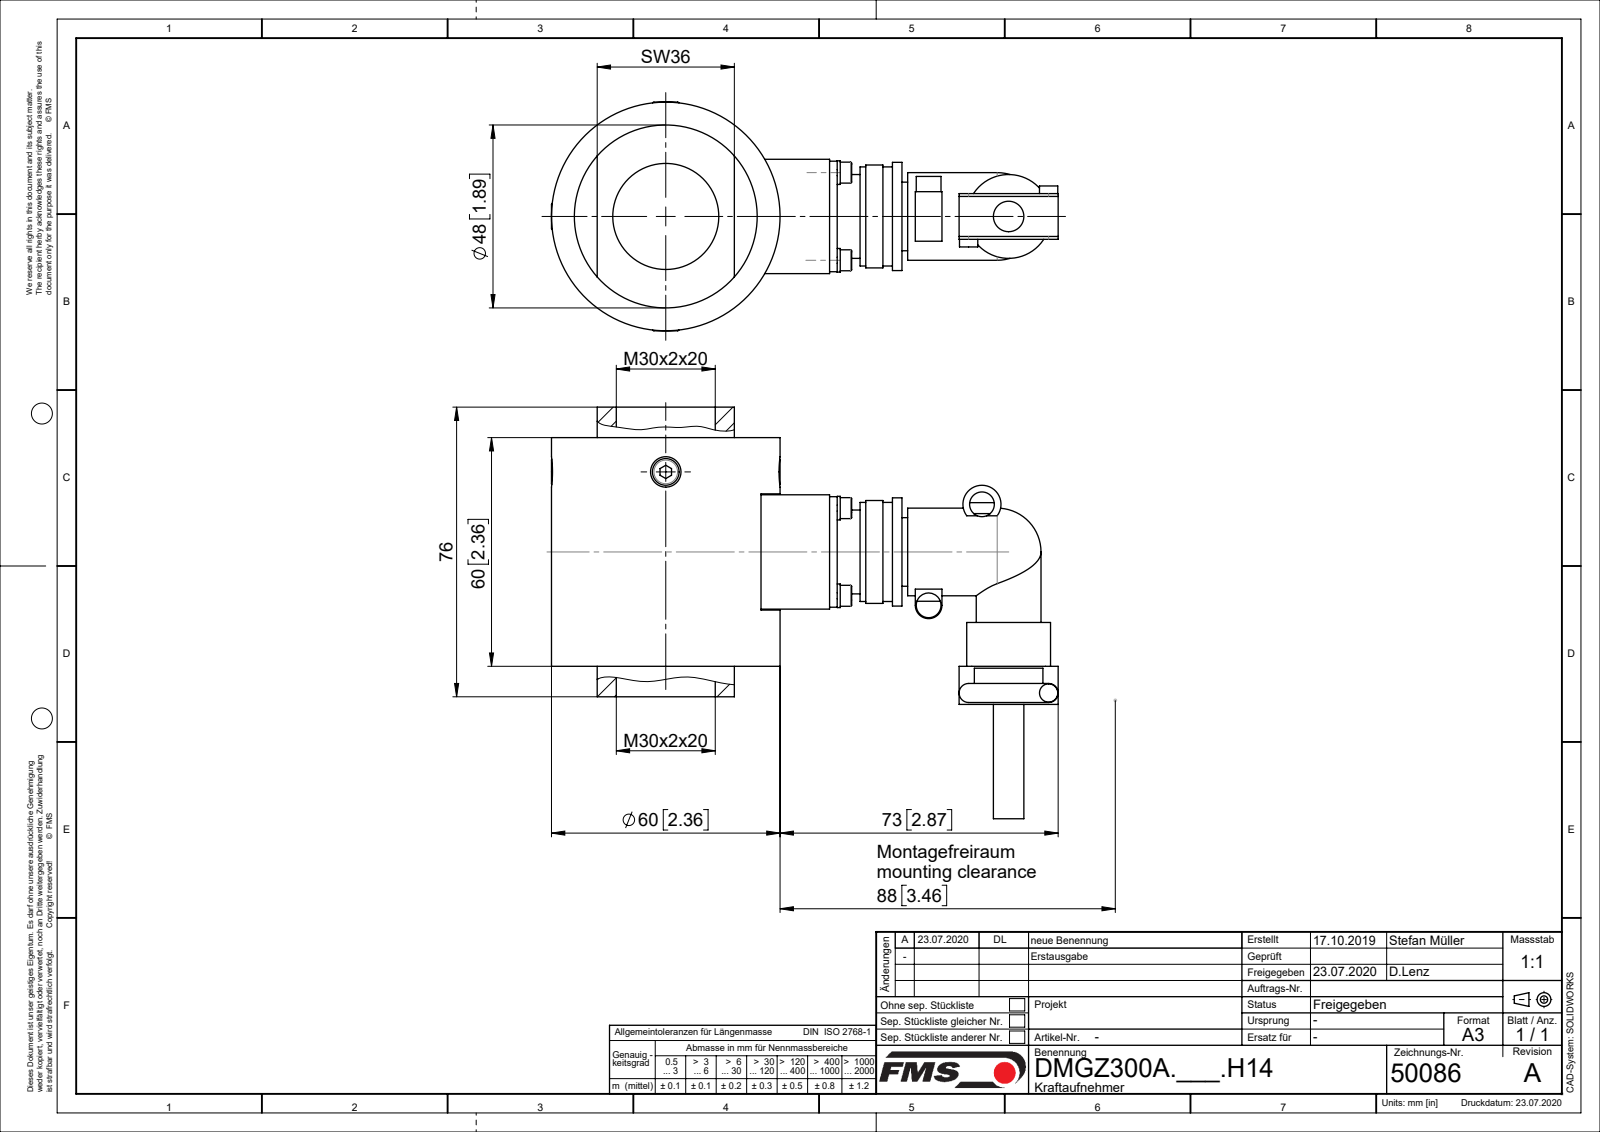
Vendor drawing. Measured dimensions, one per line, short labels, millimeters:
name: D50086; D4948204; TEIL1; D49483 (+6 more)
written by: Mechanical Desktop 2007 (CONFIG_CONTROL_DESIGN)
unit: mm
bodies: 16 solids, 300 faces (105 planar, 150 cylindrical, 45 other)
size: 133 × 108 × 60
volume: 207 305 mm³; area: 60 039 mm²
holes: 4× ⌀2.6, 4× ⌀3.2, 4× ⌀3.4, 4× ⌀3.5, 2× ⌀3.42, 2× ⌀4.3, 2× ⌀8, 1× ⌀23, 1× ⌀28.21, 1× ⌀30.5, 1× ⌀48
bosses: 4× ⌀6.2, 4× ⌀5.5, 4× ⌀3, 2× ⌀22, 2× ⌀7, 2× ⌀6.5, 2× ⌀4.8, 2× ⌀4
rounds: 2× R2.5, 1× R3.5, 1× R5
face distances: 8, 68, 20, 12, 56, 36, 48, 10, 2, 33
hole spacings: 16.26, 23, 14.92, 32.53, 34.47, 21
